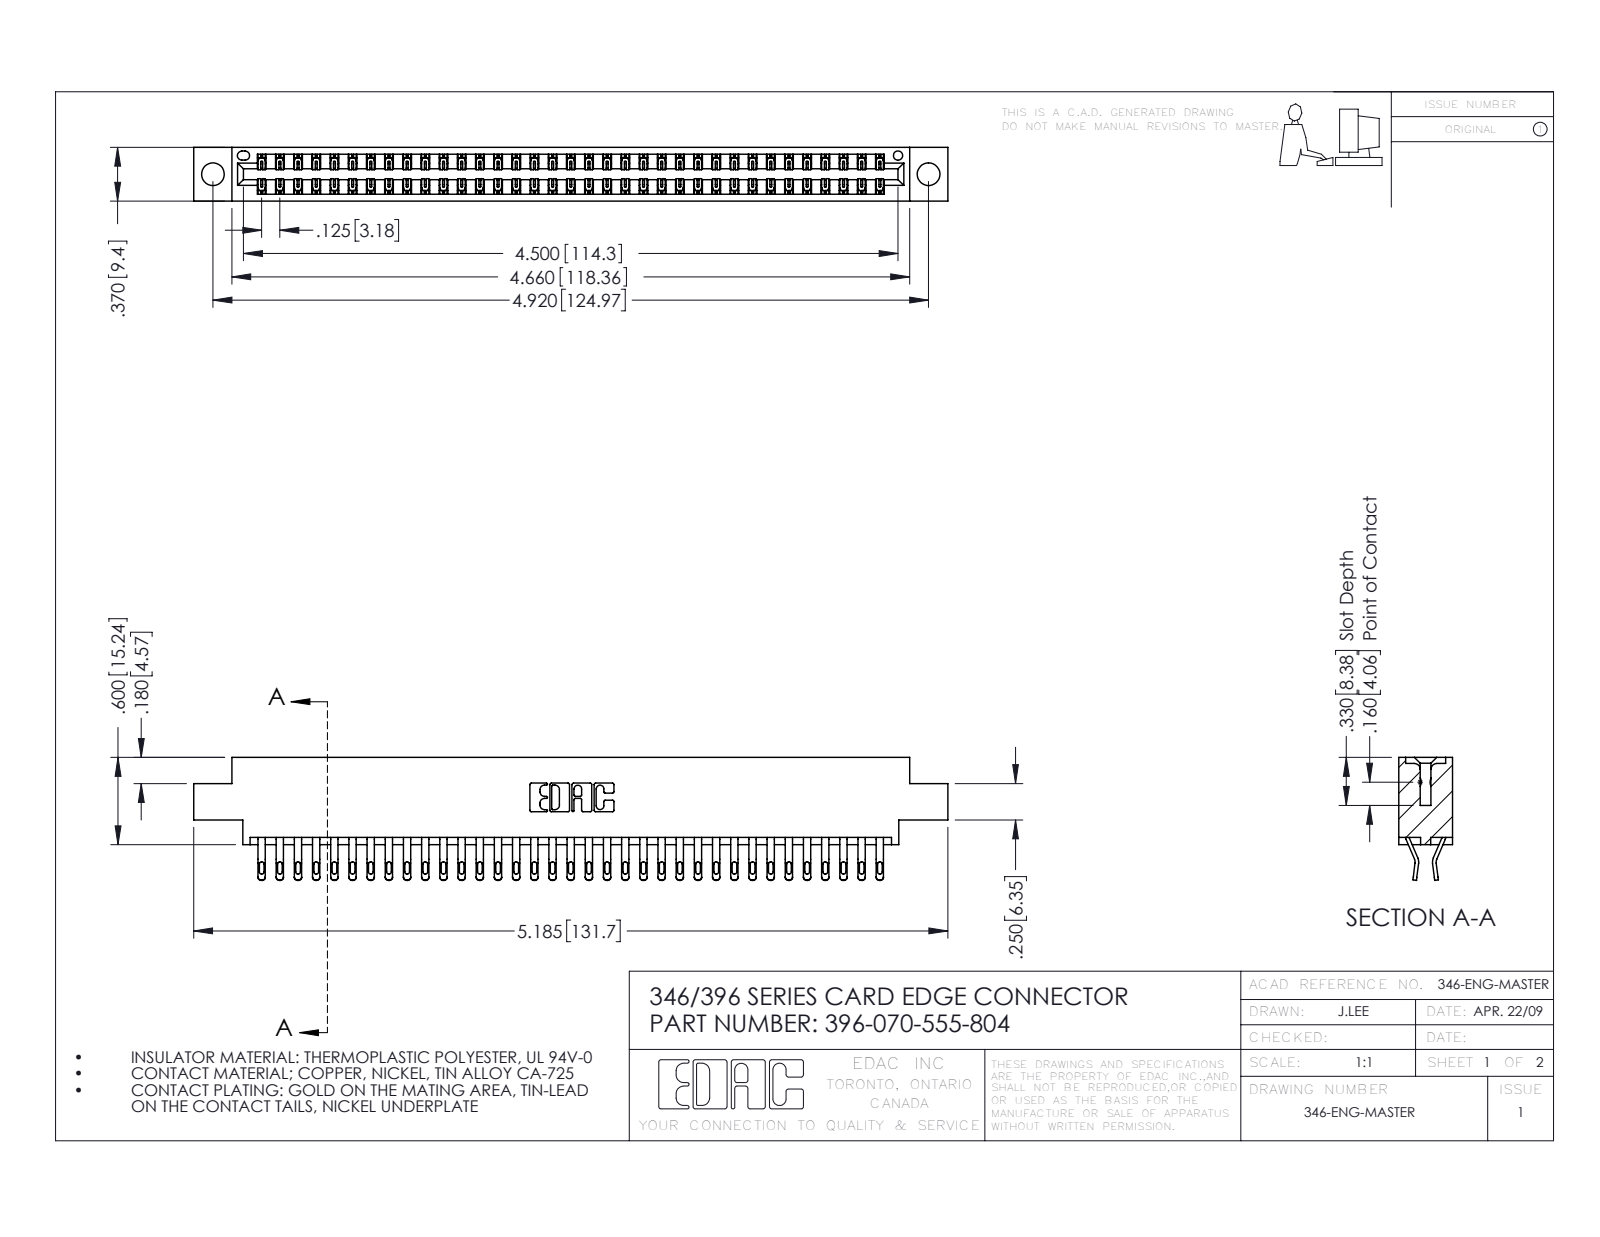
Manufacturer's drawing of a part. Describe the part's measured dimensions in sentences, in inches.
The part is named "345-292-001_555 Tail; 346 Part_0.170 Offset - 0.156 Dia-TH; 396-070-555-804". Its 3-D file was written by "SolidWorks 2016 (CONFIG_CONTROL_DESIGN)". It is 71 solids with 4186 faces: 2390 planar, 1796 cylindrical and 0 other. Overall it measures 5.185 by 0.845 by 0.37 inches. Its volume is 0.778 cubic inches and its surface area 28.1 square inches. Round holes: 2 of diameter 0.156, 1 of diameter 0.064. Partial cylindrical surfaces (rounded edges, fillets, slot ends): 140 of radius 0.016, 140 of radius 0.02, 105 of radius 0.006, 22 of radius 0.01, 6 of radius 0.007, 6 of radius 0.031, 3 of radius 0.026, 2 of radius 0.01. The main face-to-face distances are 0.048, 0.322, 0.37, 0.25, 0.025, 0.072, 0.298, 0.275, 0.148, 0.222. The hole center spacings are 0.246, 4.711, 4.92.
